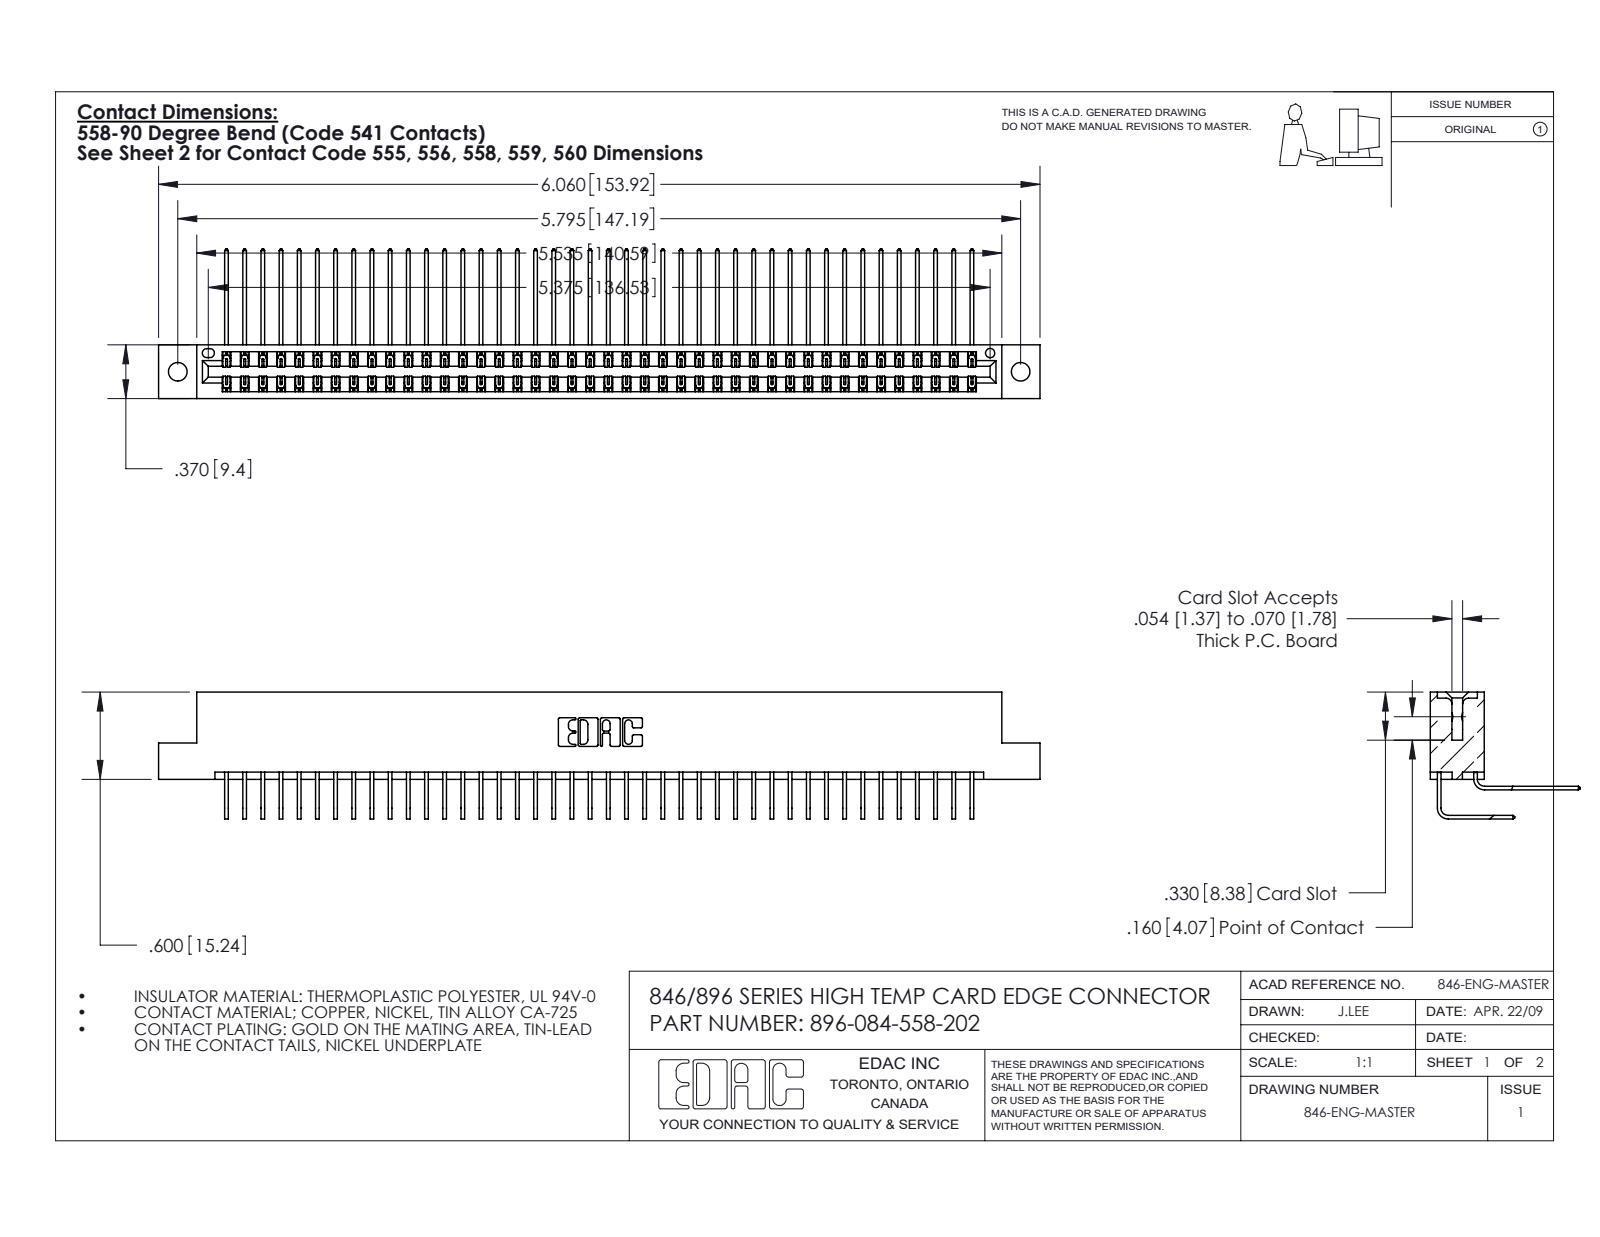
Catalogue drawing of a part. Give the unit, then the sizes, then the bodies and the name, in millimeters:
Units: millimetres
Overall size (bounding box): 153.9 × 26.2 × 22.2
Round holes (diameter × count): ⌀3.3 ×2, ⌀1.6 ×1
Partial cylindrical surfaces — rounded edges, fillets, slot ends (radius × count): R0.2 ×126, R0.3 ×22, R0.2 ×6, R0.8 ×6, R0.7 ×3, R0.4 ×2, R0.6 ×2, R0.6 ×2
Main face-to-face distances: 8.2, 1.2, 0.6, 9.4, 6.4, 7.6, 1.8, 7, 3.8, 5.6
Hole centre spacings: 6.2, 141.9, 147.2
Volume: 15 500 mm³ · Surface area: 23 300 mm²
Bodies: 85 solids, 4658 faces (3184 planar, 1474 cylindrical, 0 other)
Part name (STEP PRODUCT): 345-292-001_558 Tail - 2; 345-292-001_558 559 Tail - 1; 396-084-558-202; 346 Part_Flush Mounting Lugs - 0.128 Dia
STEP written by: SolidWorks 2016 (CONFIG_CONTROL_DESIGN)
